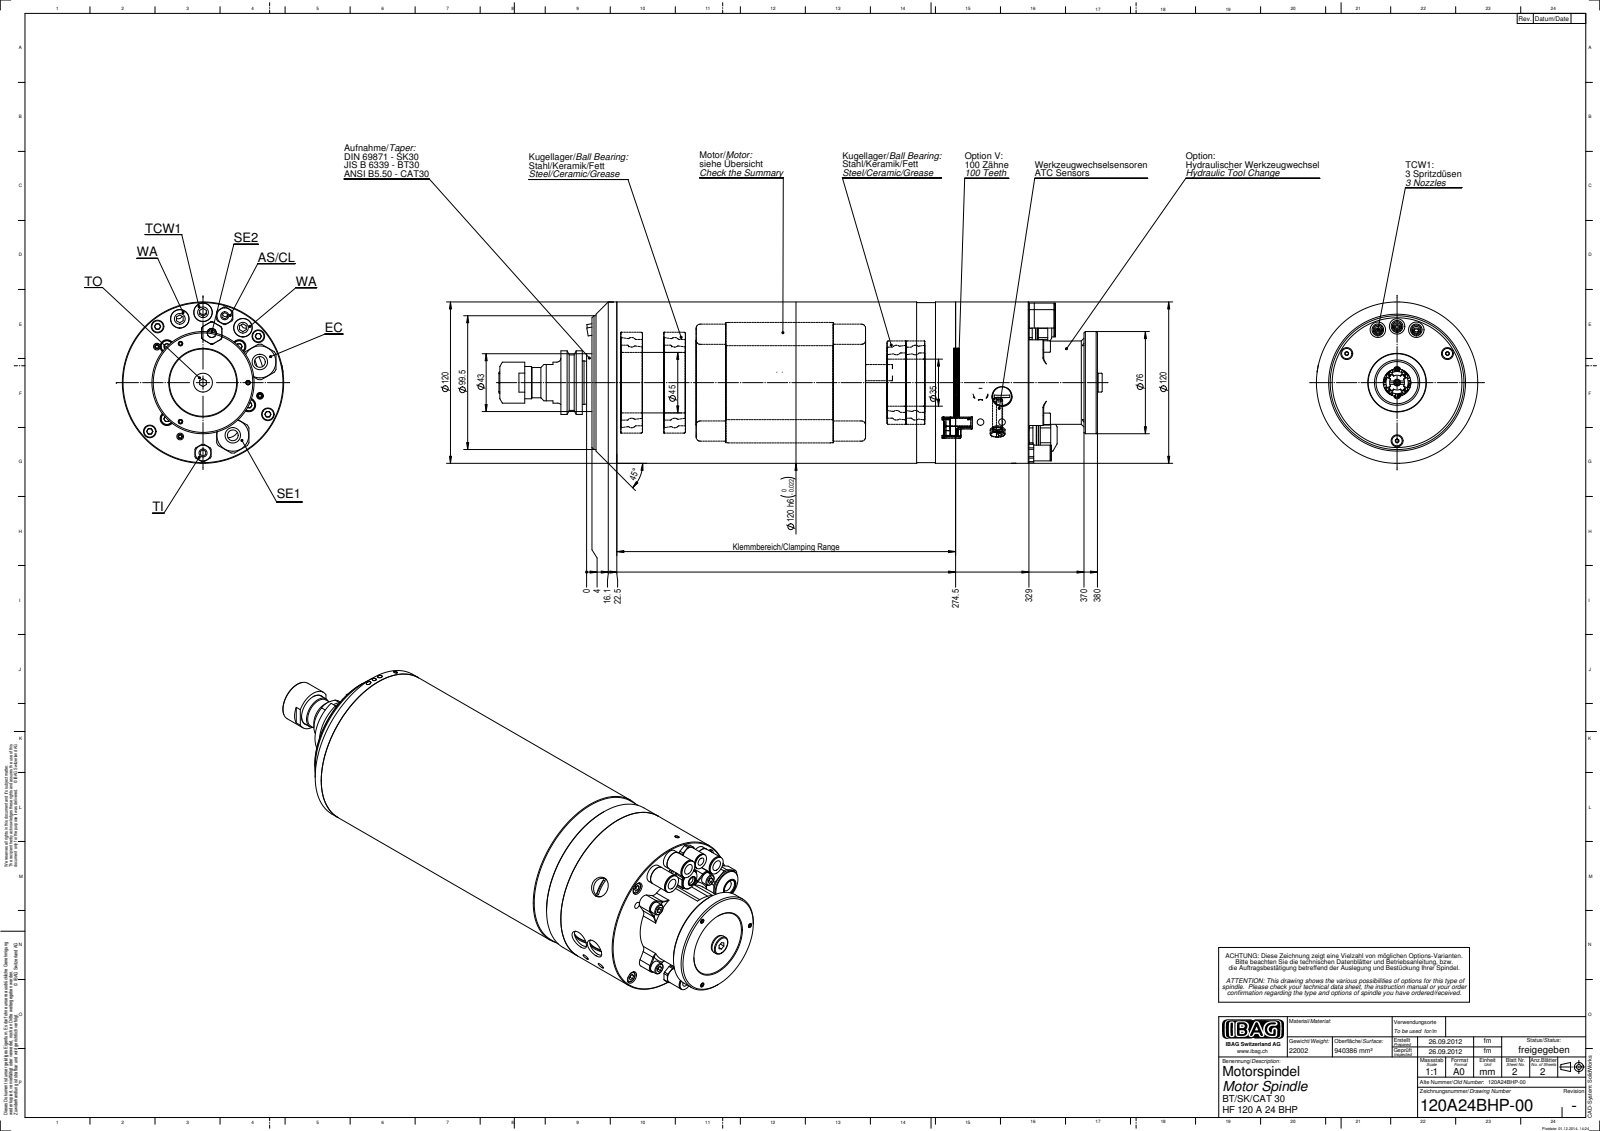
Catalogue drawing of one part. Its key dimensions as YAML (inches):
part_name: "120A24BHP-00"
step_written_by: "SolidWorks 2012 (CONFIG_CONTROL_DESIGN)"
units: inches
bodies: {solids: 0, faces: 710, planar: 281, cylindrical: 259, other: 170}
overall_size: [17.664, 4.724, 4.724]
round_holes:
  - {diameter: 0.197, count: 6}
  - {diameter: 0.315, count: 5}
  - {diameter: 0.453, count: 5}
  - {diameter: 0.591, count: 5}
  - {diameter: 0.236, count: 4}
  - {diameter: 0.37, count: 4}
  - {diameter: 0.13, count: 3}
  - {diameter: 0.177, count: 3}
  - {diameter: 0.394, count: 2}
  - {diameter: 0.264, count: 1}
  - {diameter: 1.717, count: 1}
round_bosses_or_shafts:
  - {diameter: 0.335, count: 4}
  - {diameter: 0.539, count: 3}
  - {diameter: 0.301, count: 3}
  - {diameter: 0.236, count: 3}
  - {diameter: 0.933, count: 2}
  - {diameter: 0.878, count: 2}
  - {diameter: 0.825, count: 2}
  - {diameter: 0.461, count: 2}
partial_cylinders:
  - {radius: 0.197, count: 14}
  - {radius: 0.26, count: 2}
  - {radius: 0.52, count: 2}
  - {radius: 0.236, count: 1}
  - {radius: 0.325, count: 1}
  - {radius: 0.394, count: 1}
  - {radius: 0.872, count: 1}
  - {radius: 0.984, count: 1}
face_to_face_distances: [12.067, 2.146, 9.921, 12.795, 0.728, 10.65, 0.118, 0.61, 10.531, 12.677]
hole_center_spacings: [2.114, 1.319, 1.648, 2.059, 2.284, 0.321, 0.572, 0.572]
